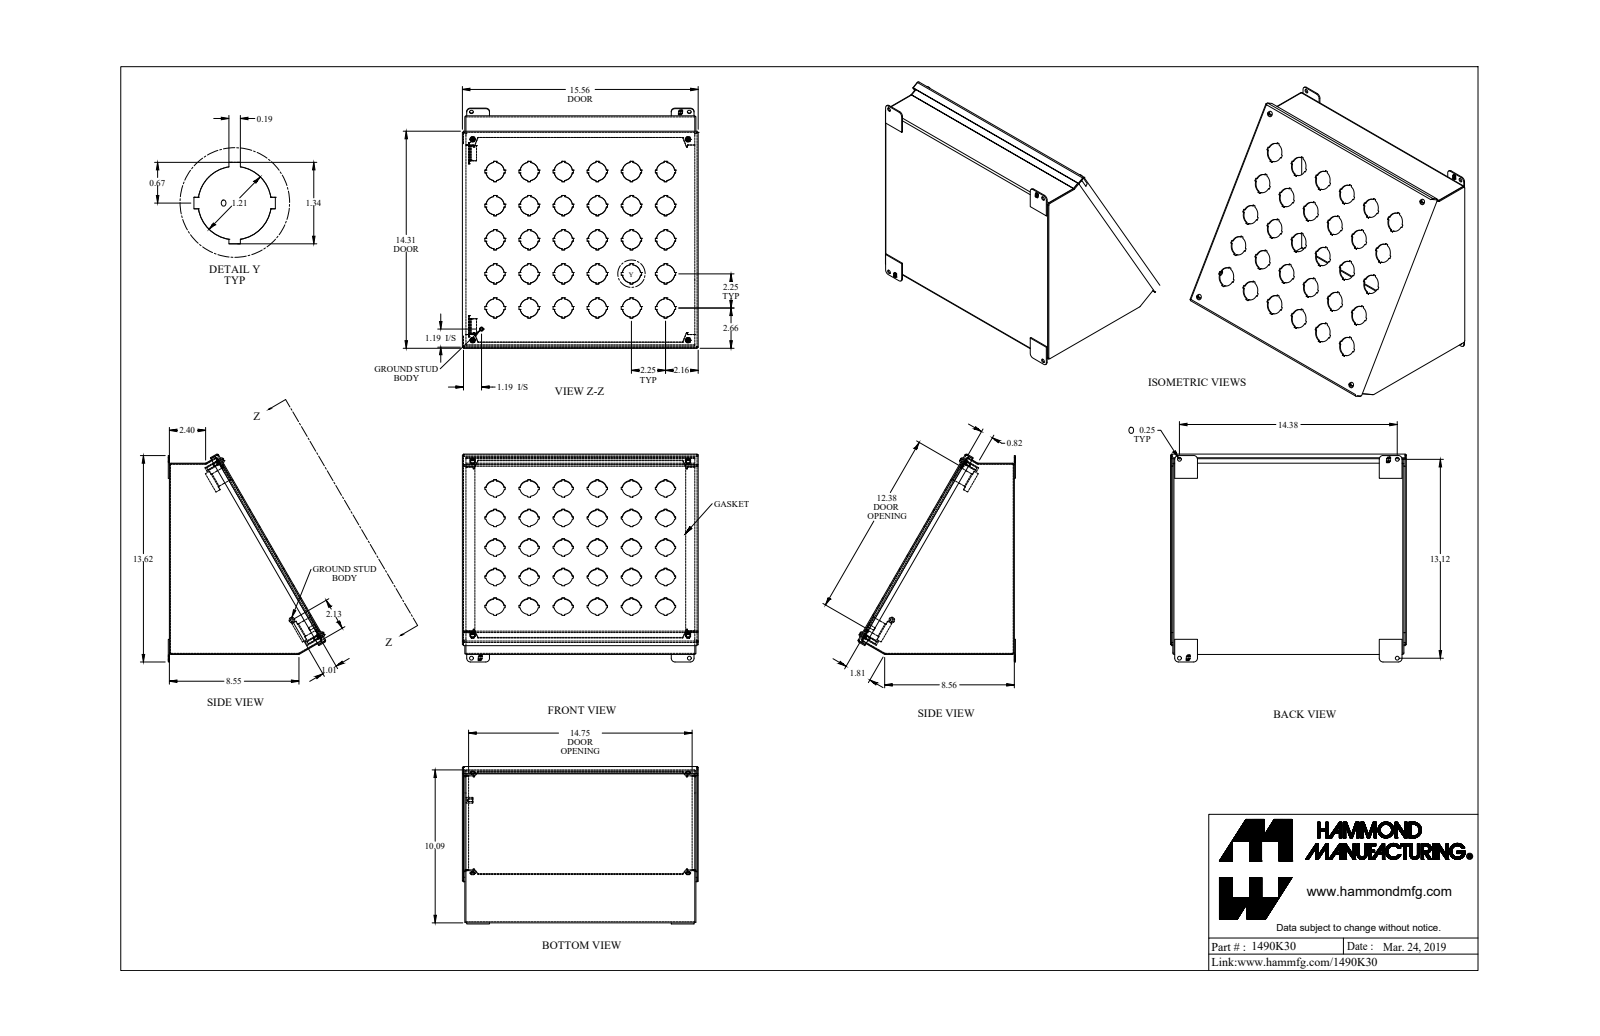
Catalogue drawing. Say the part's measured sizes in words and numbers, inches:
The part is named "1490K30_Default". Its 3-D file was written by "SolidWorks 2019 (CONFIG_CONTROL_DESIGN)". It is 28 solids with 1189 faces: 865 planar, 284 cylindrical and 40 other. Overall it measures 15.562 by 13.715 by 10.383 inches. Its volume is 65.87 cubic inches and its surface area 1 750 square inches. Round holes: 30 of diameter 1.21, 8 of diameter 0.25, 4 of diameter 0.159, 1 of diameter 0.156. Round bosses or shafts: 4 of diameter 0.39, 4 of diameter 0.275, 4 of diameter 0.19, 4 of diameter 0.148, 1 of diameter 0.375, 1 of diameter 0.25, 1 of diameter 0.188. Partial cylindrical surfaces (rounded edges, fillets, slot ends): 18 of radius 0.108, 12 of radius 0.036, 8 of radius 0.029, 8 of radius 0.086, 8 of radius 0.25, 4 of radius 0.125, 4 of radius 0.16, 4 of radius 0.171. The main face-to-face distances are 0.072, 0.072, 15.178, 15.106, 15.25, 12.543, 12.615, 12.472, 0.259, 0.187. The hole center spacings are 5.031, 2.25, 3.182, 7.115, 8.112, 4.5, 6.364, 6.75.
